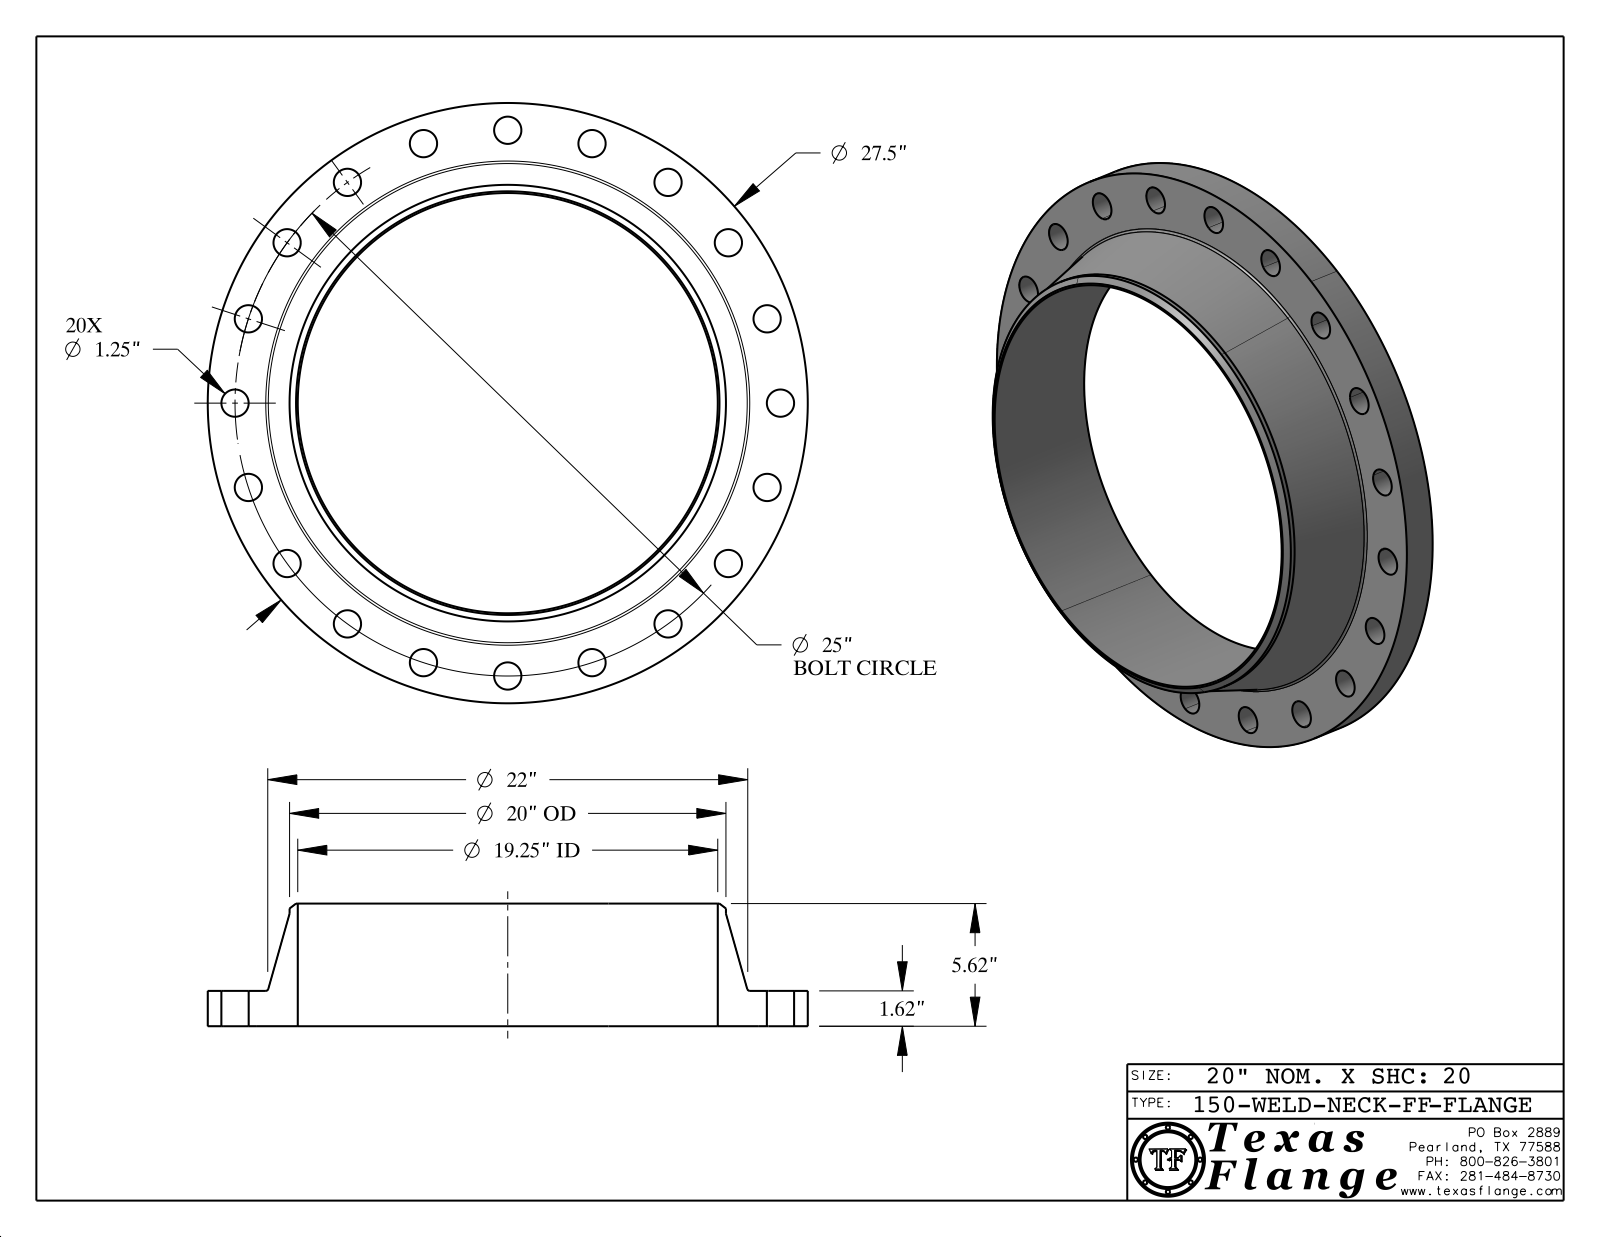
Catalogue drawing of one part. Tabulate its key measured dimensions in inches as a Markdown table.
| quantity | value |
| --- | --- |
| part name | 150-WELD-NECK-FF |
| STEP written by | CATIA V5 STEP AP214 (AUTOMOTIVE_DESIGN) |
| units | inches |
| bodies | 1 solid, 441 faces (369 planar, 66 cylindrical, 6 other) |
| overall size | 27.5 × 27.5 × 5.62 |
| volume | 656.3 in³ |
| surface area | 1 358 in² |
| round holes (diameter × count) | 1.25 × 20, 0.495 × 1, 19.25 × 1 |
| round bosses / shafts (diameter × count) | 0.03 × 8, 27.5 × 1, 20 × 1, 0.39 × 1 |
| main face-to-face distances | 1.62, 5.62, 4, 1.605, 0.015, 4.015, 0.148, 0.145, 0.027, 0.096 |
| hole center spacings | 12.5, 14.694, 17.678, 20.225, 23.776, 24.692, 11.35, 22.275 |
